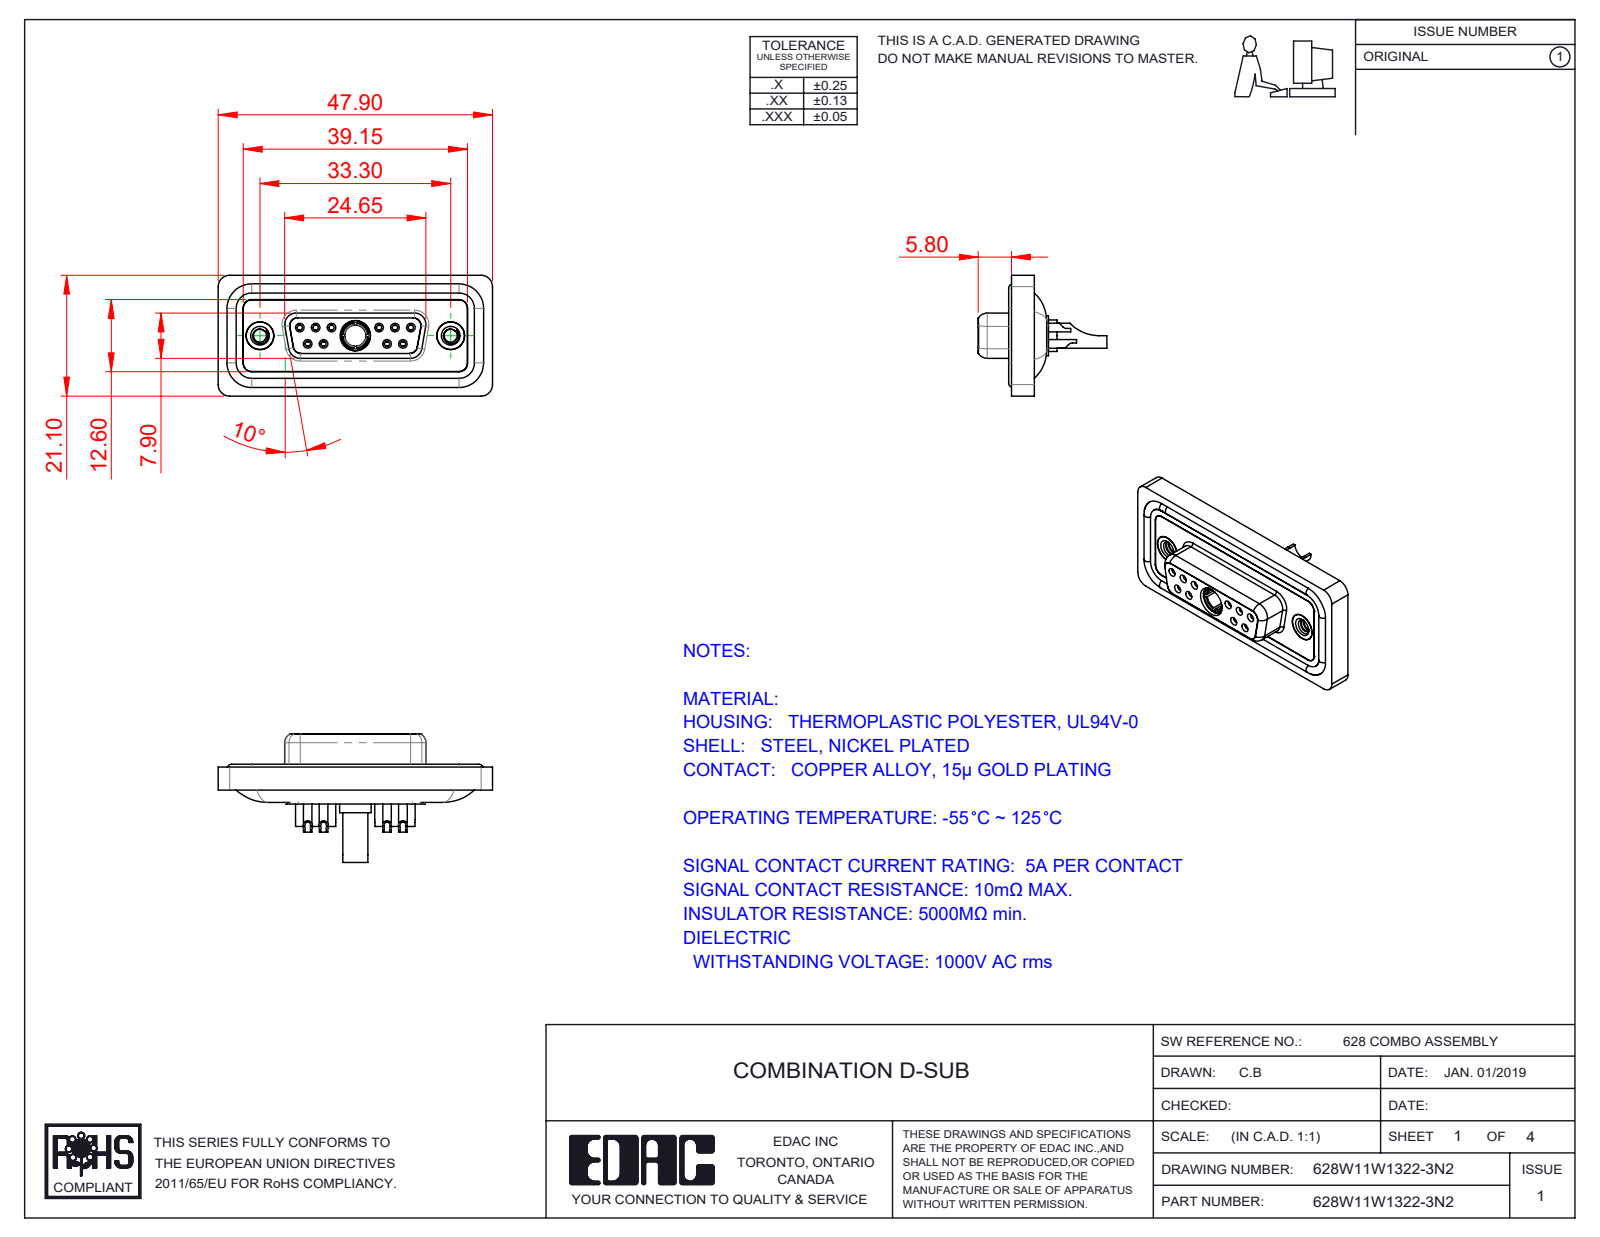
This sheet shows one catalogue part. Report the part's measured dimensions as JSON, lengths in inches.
{"part_name": "628Combo Housing_11W1; 628Combo Contact Row 2_22; 628Combo Threaded Rivet_2; 628Combo Shell Front_15 Contacts (+5 more)", "step_written_by": "SolidWorks 2023 (CONFIG_CONTROL_DESIGN)", "units": "inches", "bodies": {"solids": 19, "faces": 1016, "planar": 307, "cylindrical": 424, "other": 285}, "overall_size": [1.886, 0.884, 0.831], "volume_in3": 0.376, "surface_area_in2": 15.87, "round_holes": [[0.035, 10], [0.039, 10], [0.043, 10], [0.059, 10], [0.079, 10], [0.067, 6], [0.063, 4], [0.191, 3], [0.089, 2], [0.157, 2], [0.159, 2], [0.197, 2]], "round_bosses_or_shafts": [[0.087, 10], [0.063, 10], [0.195, 2], [0.189, 2], [0.217, 1], [0.205, 1], [0.195, 1], [0.187, 1]], "partial_cylinders_radius": [[0.059, 22], [0.079, 20], [0.053, 12], [0.063, 8], [0.039, 6], [0.01, 4], [0.02, 4], [0.024, 4]], "face_to_face_distances": [0.016, 0.063, 0.071, 0.114, 0.02, 0.043, 0.222, 0.293, 0.26, 0.278], "hole_center_spacings": [0.124, 0.109, 0.545, 0.436, 0.654, 0.198, 0.198, 0.218]}
